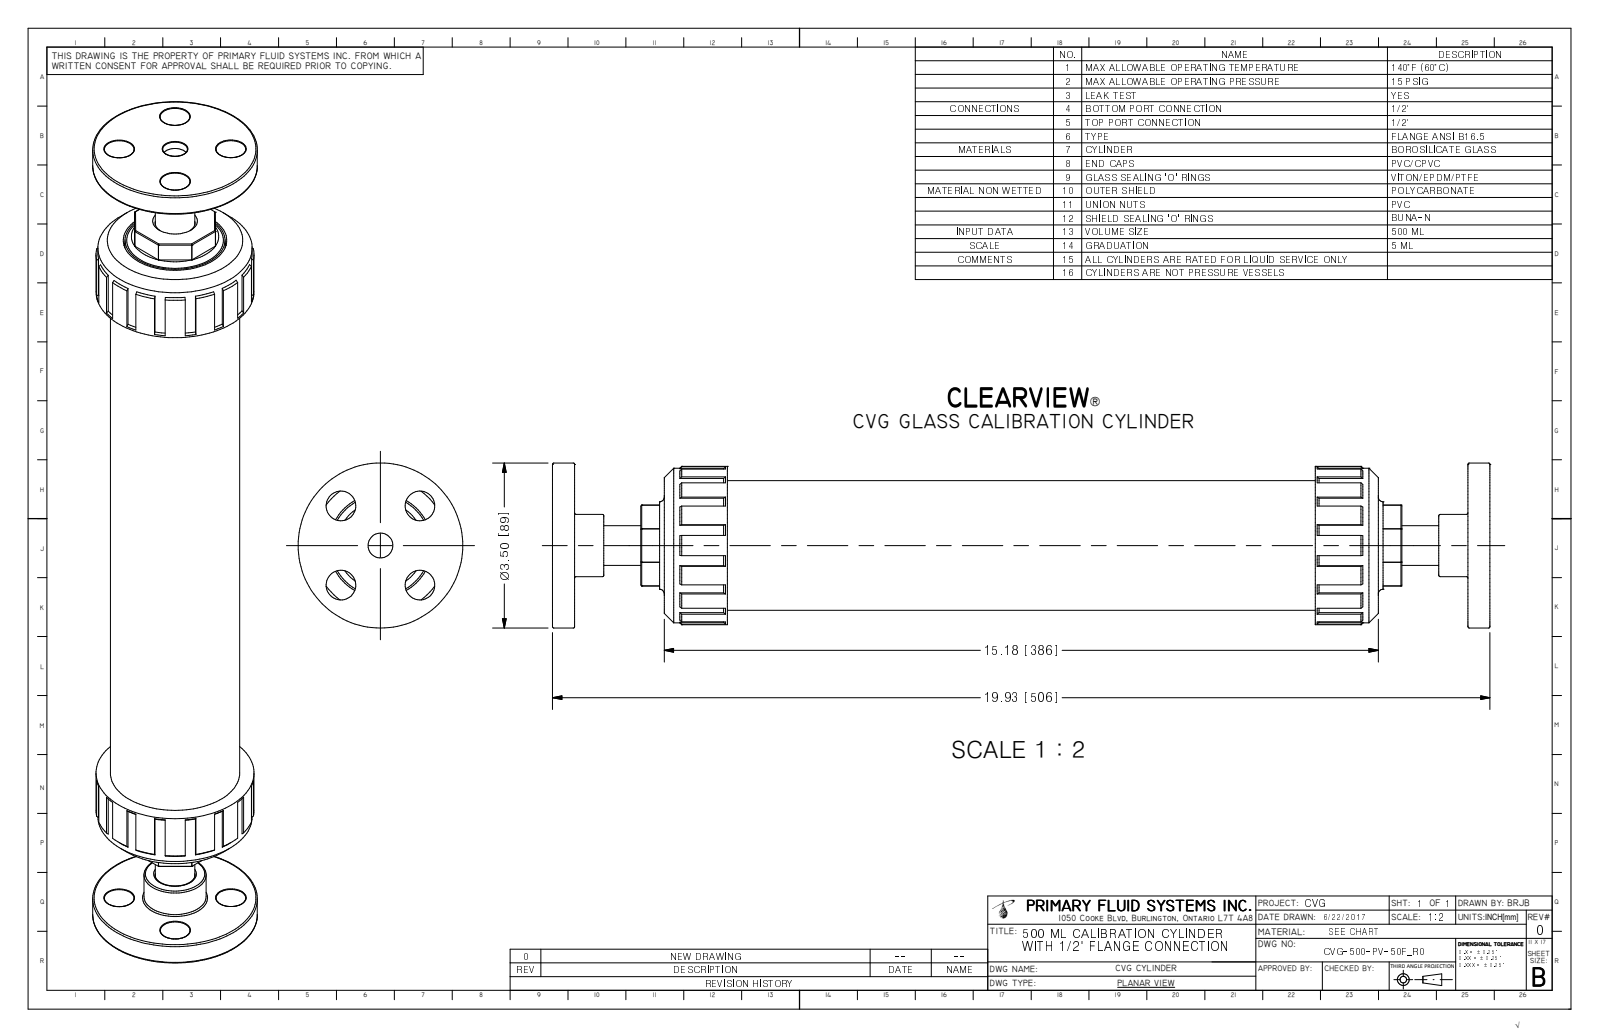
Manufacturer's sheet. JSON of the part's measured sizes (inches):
{"part_name": "CVG-500-PV-50F_R0", "step_written_by": "Autodesk Inventor 2009 (AUTOMOTIVE_DESIGN)", "units": "inches", "bodies": {"solids": 1, "faces": 330, "planar": 96, "cylindrical": 40, "other": 194}, "overall_size": [19.93, 3.5, 3.5], "volume_in3": 108.9, "surface_area_in2": 250.8, "round_holes": [[0.63, 4], [0.526, 1]], "round_bosses_or_shafts": [[3.5, 1], [2.75, 1], [2.661, 1], [2.126, 1], [1.32, 1]], "partial_cylinders_radius": [[0.928, 1]], "face_to_face_distances": [19.93, 0.47, 19.46, 19.46, 18.99, 0.47, 1.405, 17.585, 1.715, 18.055], "hole_center_spacings": [1.188, 1.68, 2.375]}
